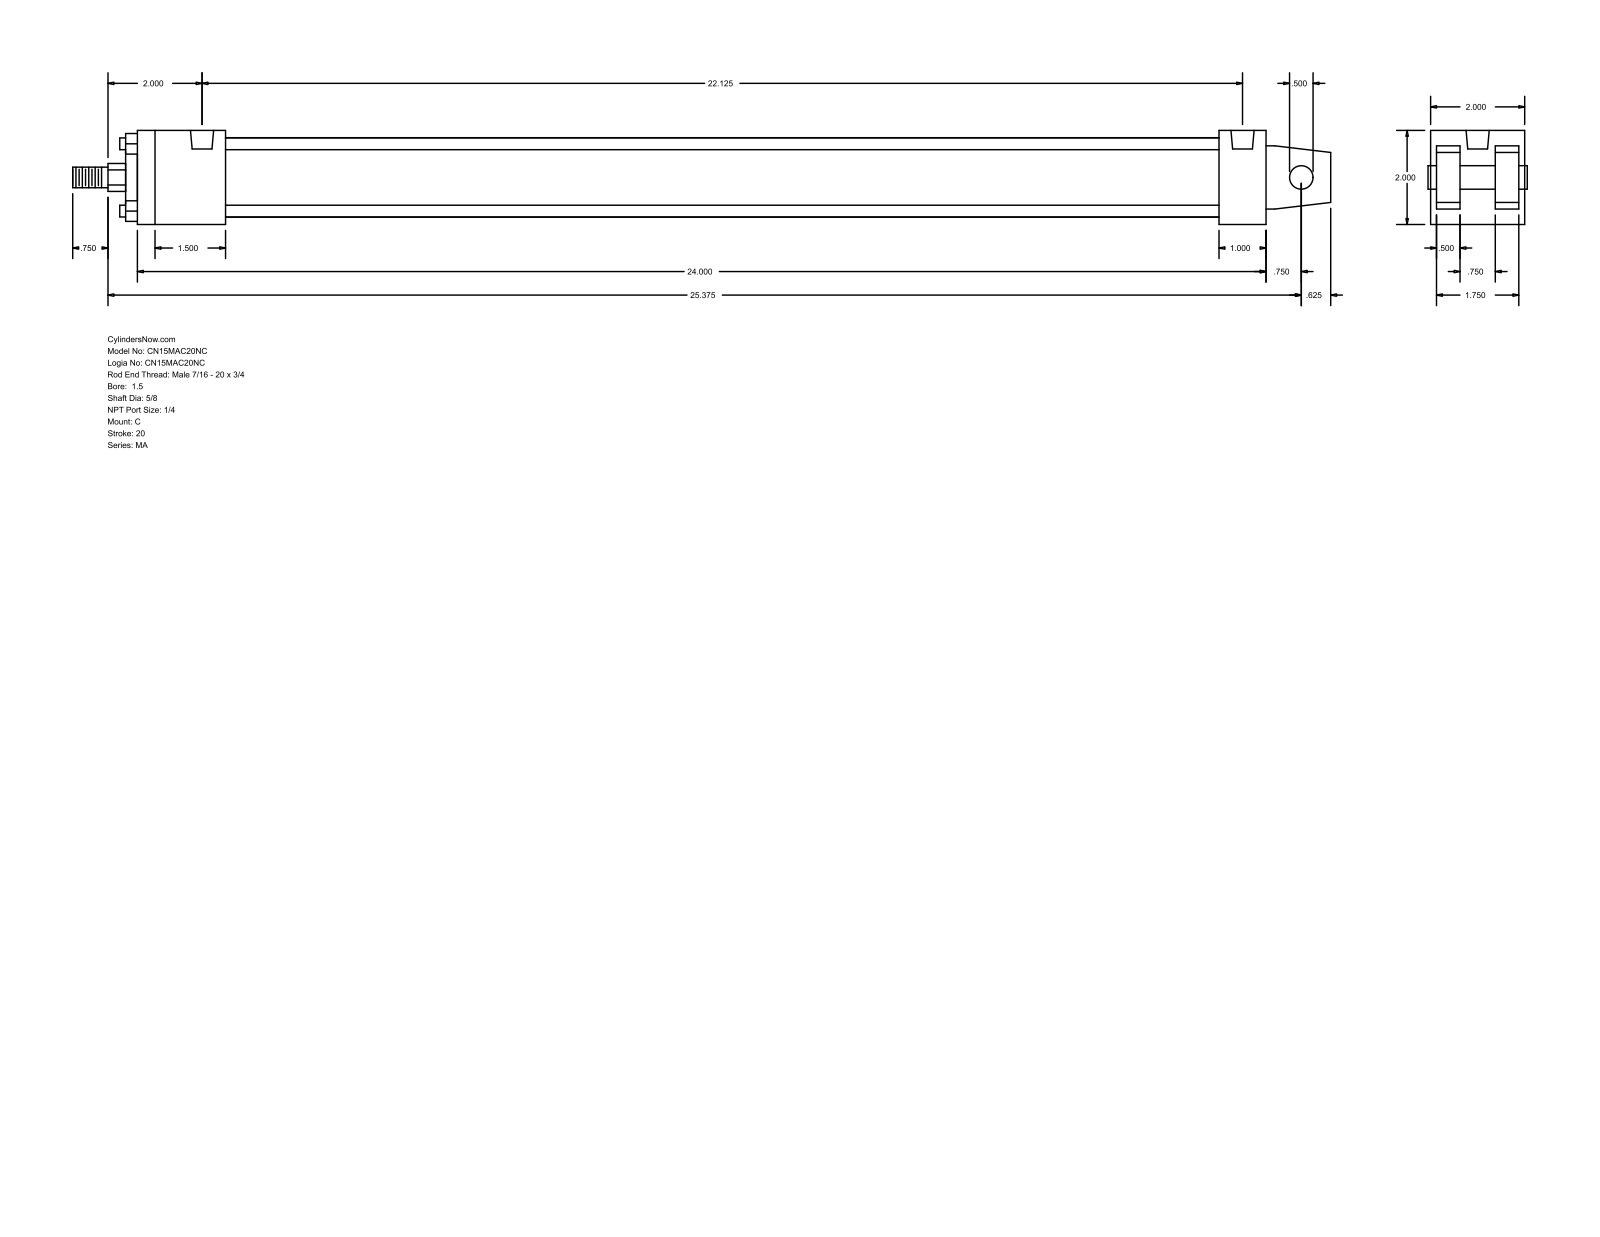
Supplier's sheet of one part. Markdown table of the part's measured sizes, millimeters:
| quantity | value |
| --- | --- |
| part name | MA_C__0150_0.625 |
| STEP written by | GSSL Pune (CONFIG_CONTROL_DESIGN) |
| units | millimeters |
| bodies | 0 solids, 103 faces (76 planar, 27 cylindrical, 0 other) |
| overall size | 679.45 × 50.8 × 50.8 |
| round holes (diameter × count) | 7.94 × 4, 12.49 × 2 |
| round bosses / shafts (diameter × count) | 6.35 × 4, 42.93 × 1, 28.57 × 1, 15.88 × 1, 12.7 × 1, 11.11 × 1 |
| partial cylindrical surfaces (radius × count) | 7.54 × 1 |
| main face-to-face distances | 50.8, 12.7, 34.93, 15.87, 3.17, 47.63, 31.76, 609.6, 25.4, 584.2 |
| hole center spacings | 561.97 |
